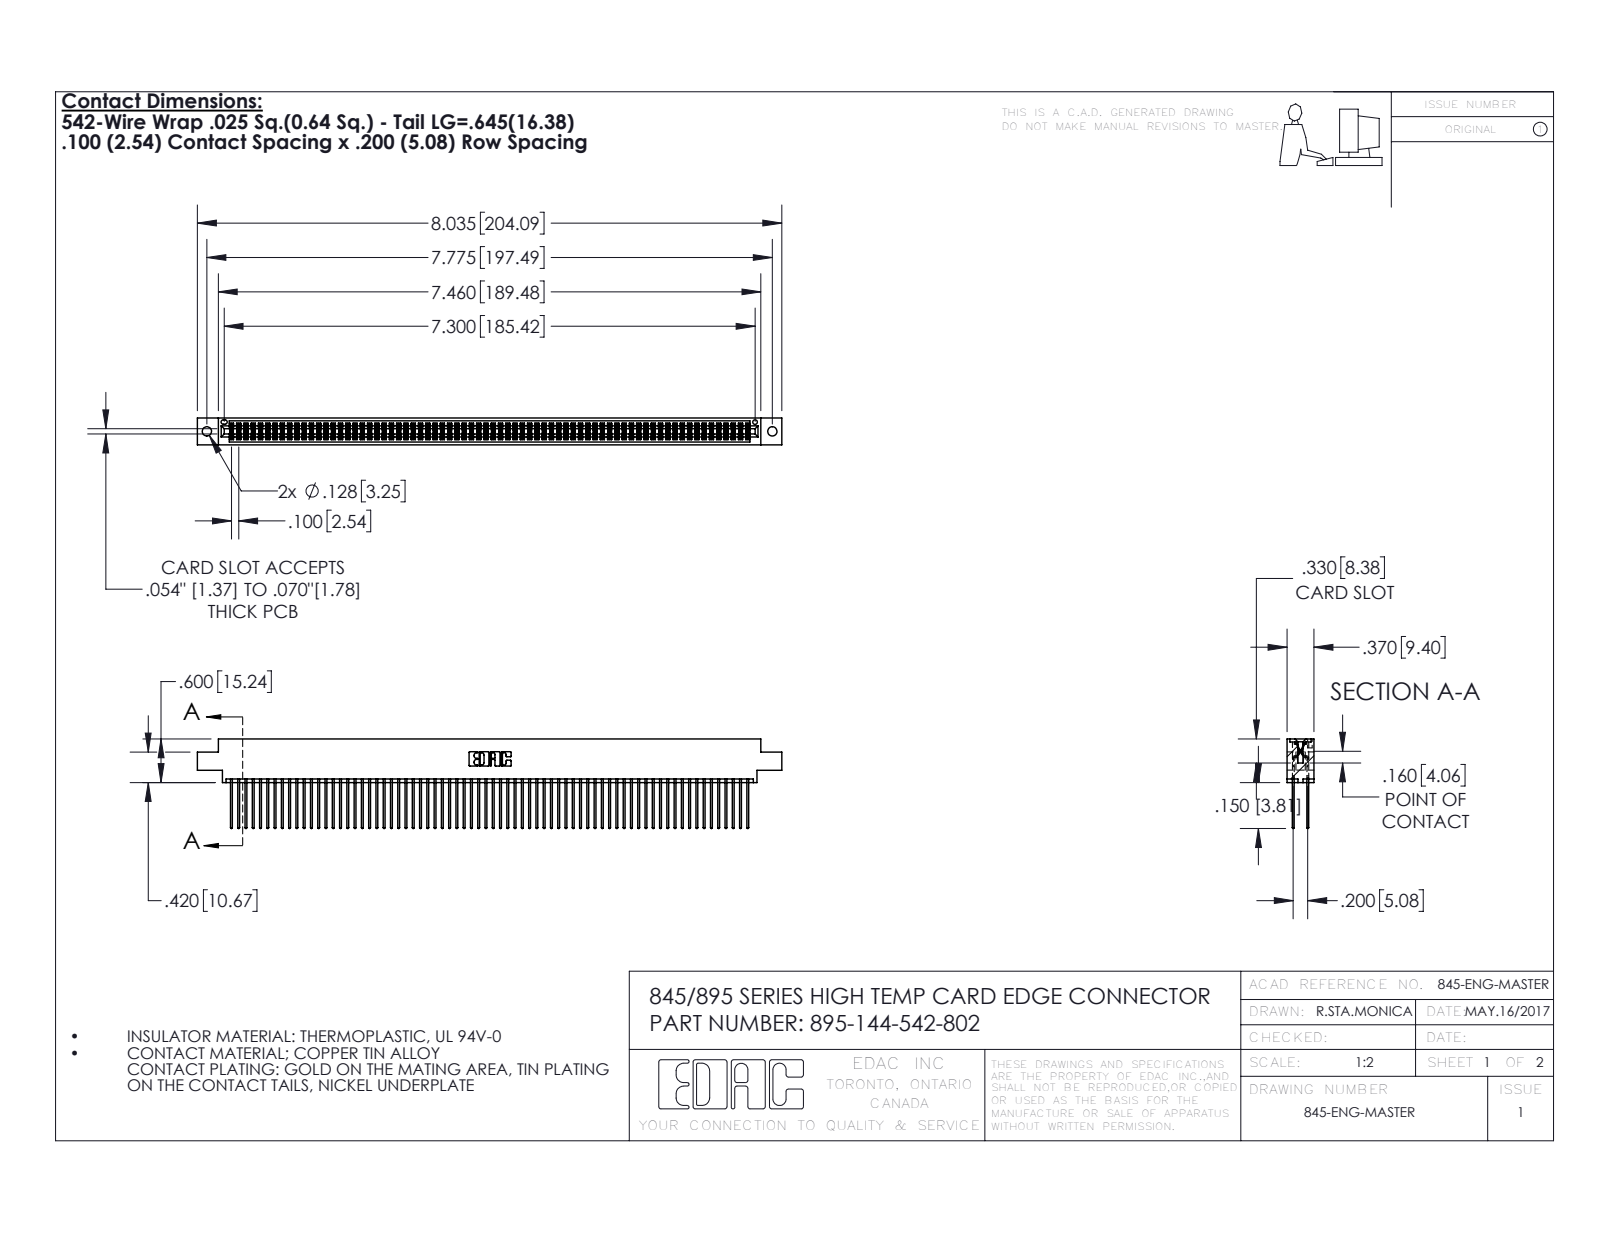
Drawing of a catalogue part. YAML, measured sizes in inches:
part_name: "345-292-001_345-293-142; 345 Part_0.170 Offset - 0.128 Dia; 395-144-542-802"
step_written_by: "SolidWorks 2016 (CONFIG_CONTROL_DESIGN)"
units: inches
bodies: {solids: 145, faces: 7330, planar: 4836, cylindrical: 2494, other: 0}
overall_size: [8.035, 1.232, 0.37]
volume: 1.259
surface_area: 52.82
round_holes:
  - {diameter: 0.128, count: 2}
  - {diameter: 0.064, count: 1}
partial_cylinders:
  - {radius: 0.006, count: 216}
  - {radius: 0.01, count: 144}
  - {radius: 0.01, count: 22}
  - {radius: 0.007, count: 6}
  - {radius: 0.031, count: 6}
  - {radius: 0.026, count: 3}
  - {radius: 0.014, count: 2}
  - {radius: 0.019, count: 2}
face_to_face_distances: [0.298, 0.072, 0.2, 0.098, 0.272, 0.025, 0.225, 0.37, 0.175, 0.149]
hole_center_spacings: [0.27, 7.539, 7.775]
